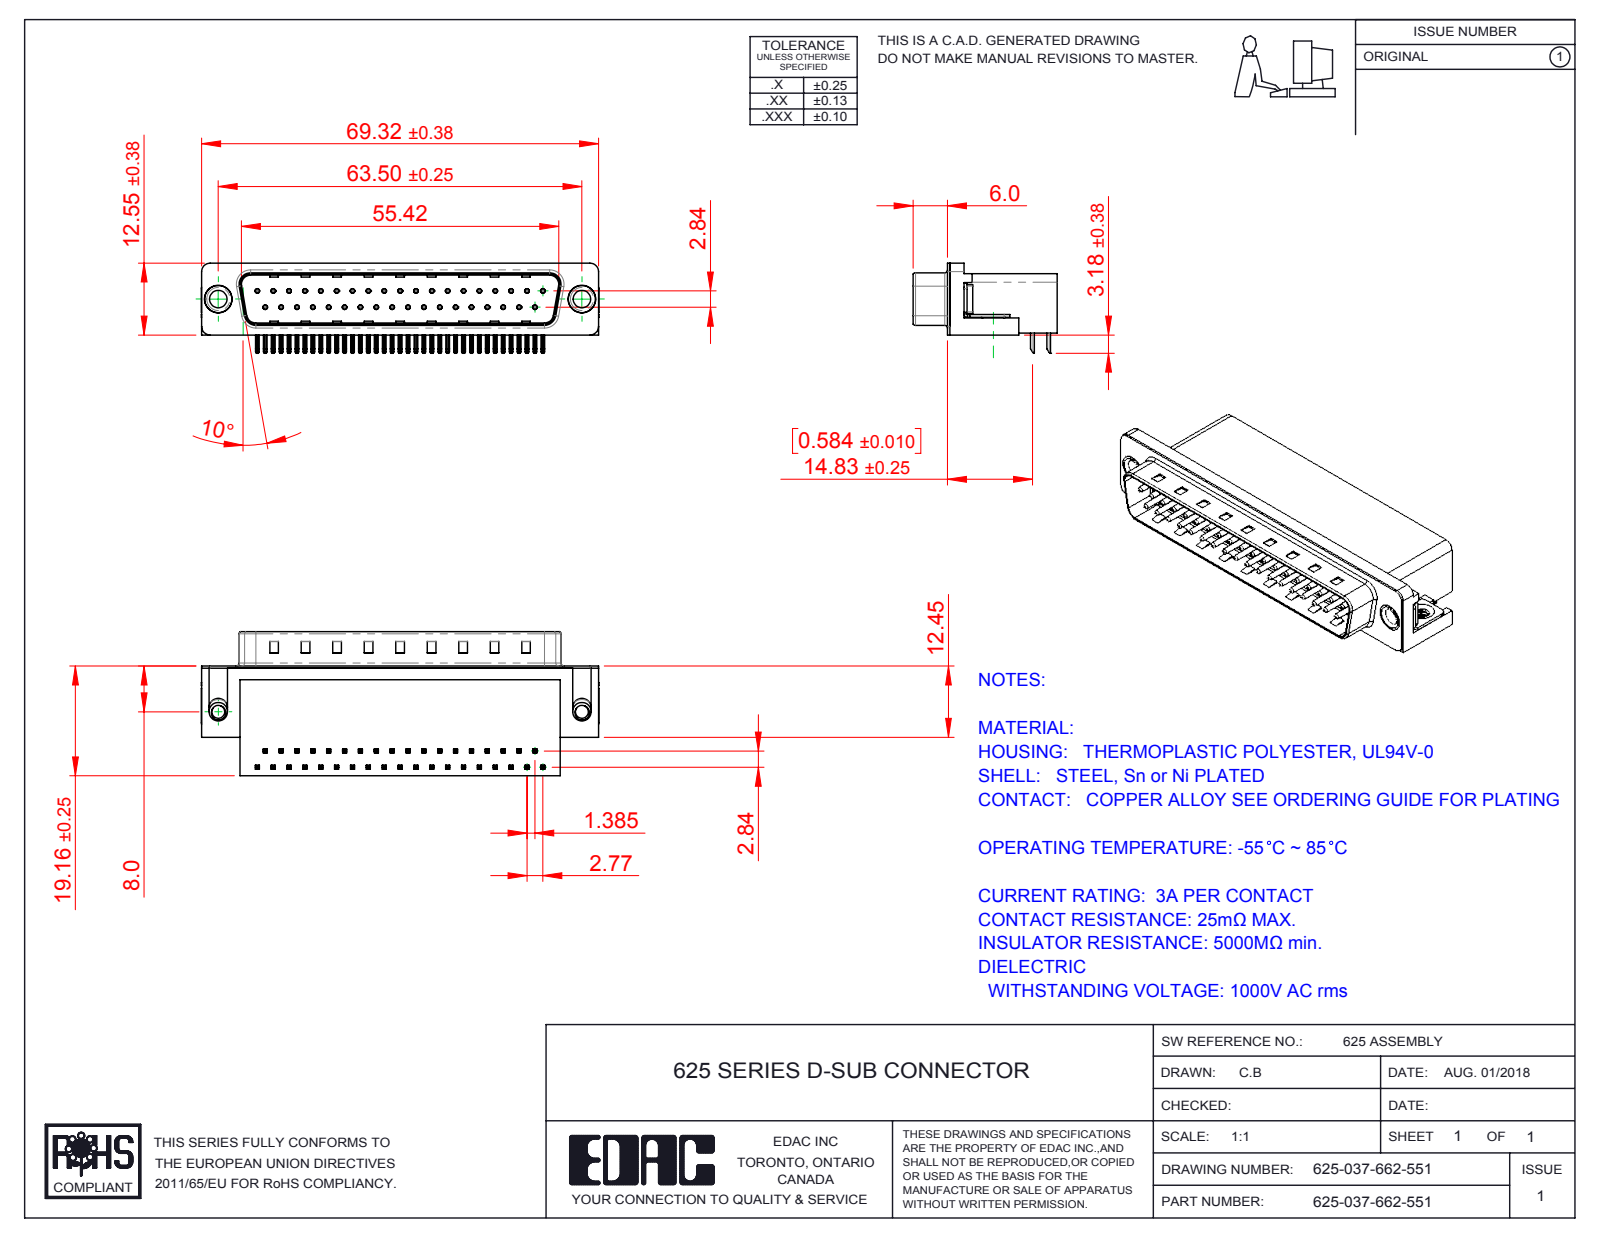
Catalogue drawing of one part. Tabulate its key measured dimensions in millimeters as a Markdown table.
| quantity | value |
| --- | --- |
| part name | 625 Contact Top; 625 Shell_37 Socket; 625 Housing_37 Socket; 625 4-40 Threaded Board Mount (+3 more) |
| STEP written by | SolidWorks 2016 (CONFIG_CONTROL_DESIGN) |
| units | millimeters |
| bodies | 43 solids, 3193 faces (2015 planar, 911 cylindrical, 267 other) |
| overall size | 69.4 × 25.16 × 15.73 |
| volume | 12 599 mm³ |
| surface area | 11 810 mm² |
| round holes (diameter × count) | 0.35 × 37, 0.8 × 37, 2.26 × 2, 3.05 × 2, 4 × 2, 4.8 × 2, 5 × 2 |
| round bosses / shafts (diameter × count) | 0.75 × 37, 4.9 × 2, 4.75 × 2, 3.85 × 2, 3.26 × 2 |
| partial cylindrical surfaces (radius × count) | 0.25 × 156, 0.12 × 74, 1 × 16, 0.5 × 9, 1.6 × 8, 1.5 × 7, 0.9 × 4, 2 × 4 |
| main face-to-face distances | 10.34, 0.4, 18.76, 8.76, 19.16, 2.84, 2.09, 10.1, 1.74, 8.36 |
| hole center spacings | 3.16, 2.77, 5.54, 8.31, 11.08, 13.85, 19.39, 22.16 |
